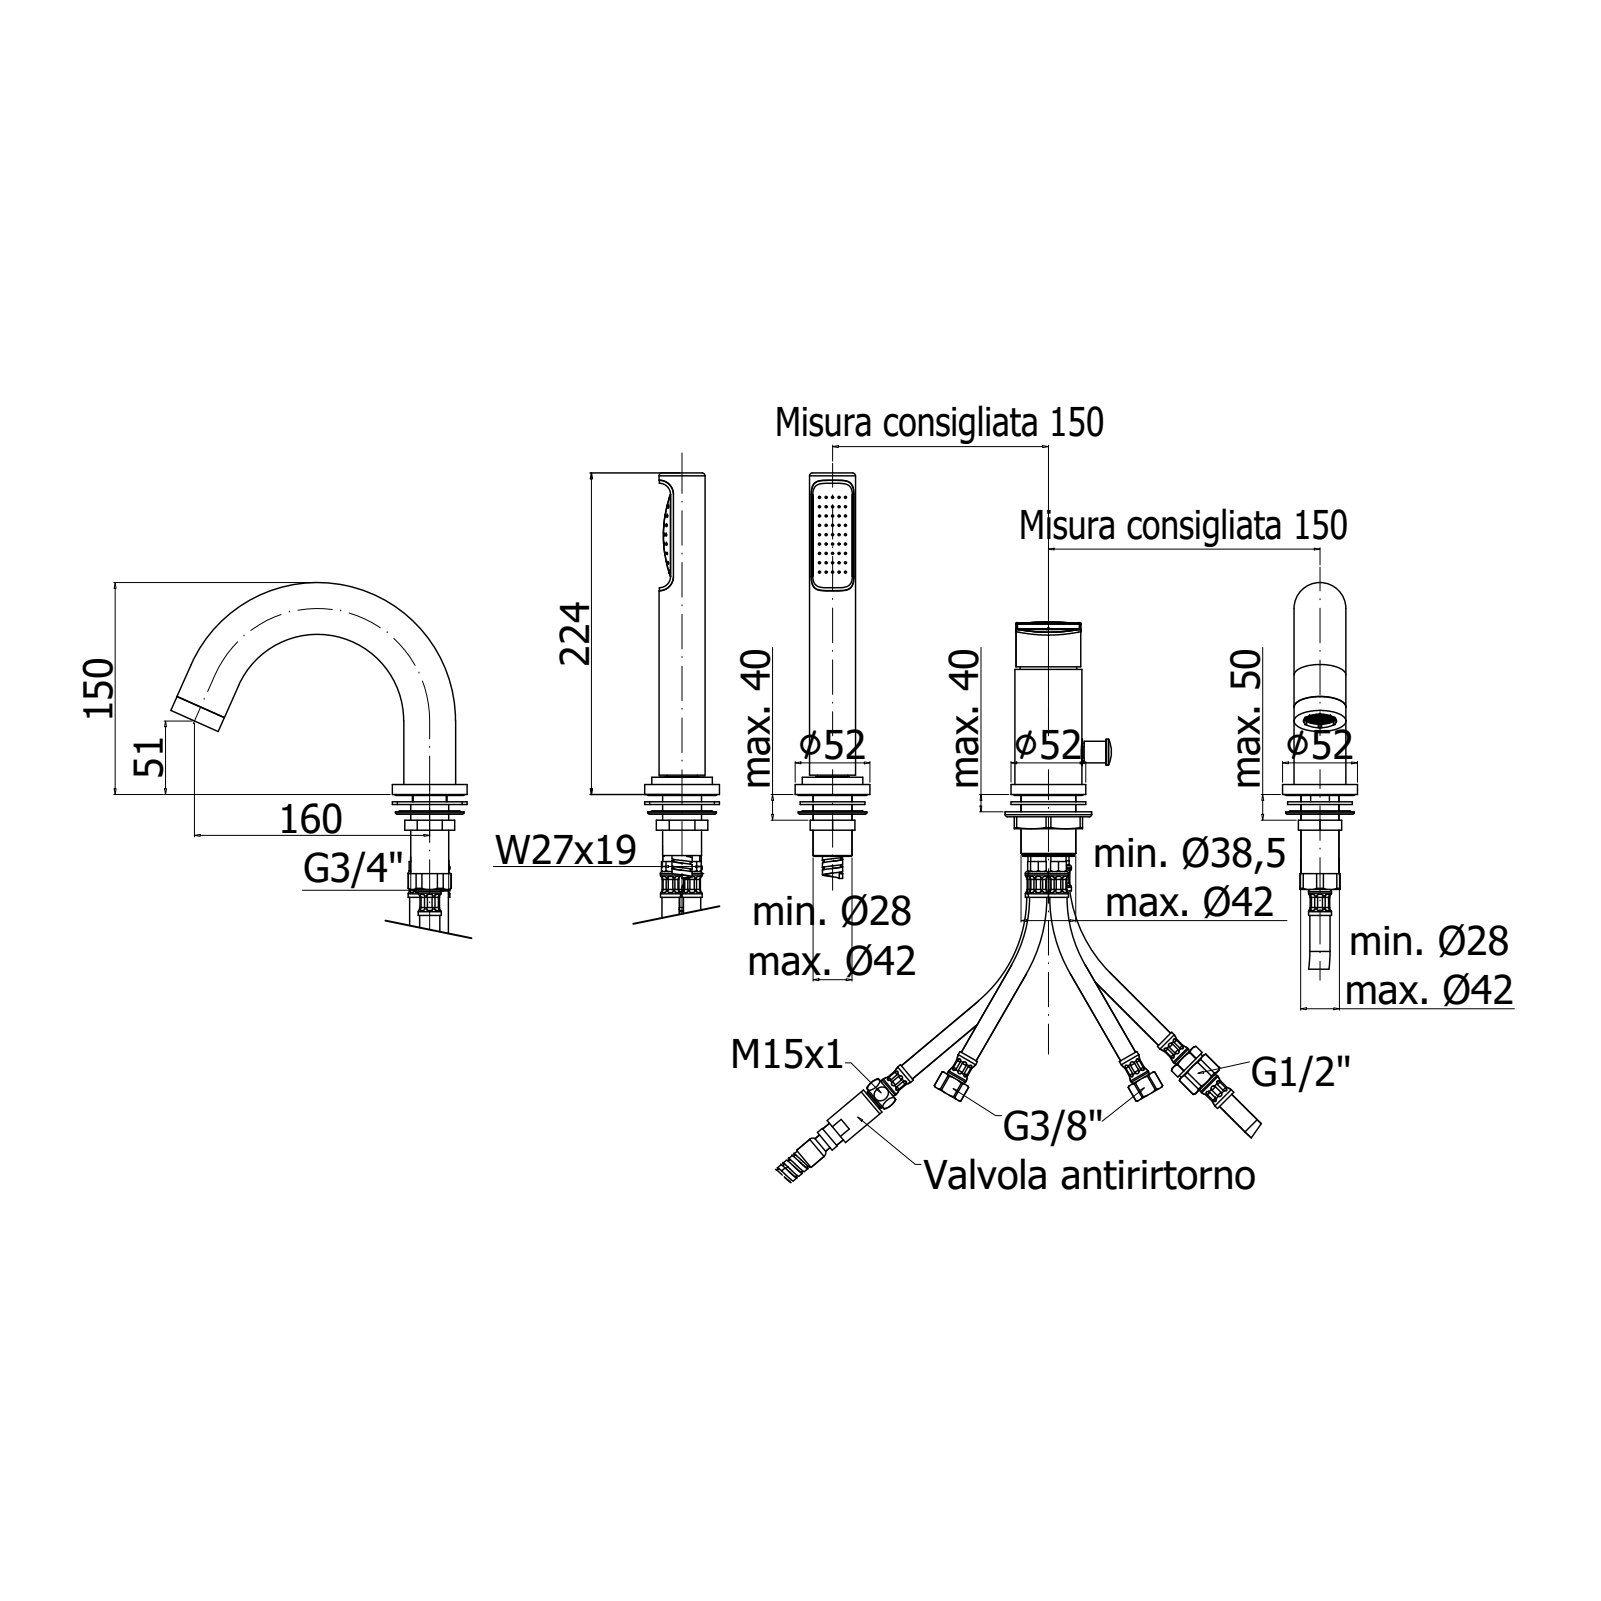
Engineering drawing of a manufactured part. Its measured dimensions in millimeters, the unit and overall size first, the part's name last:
Units: millimetres
Overall size (bounding box): 352 × 237.5 × 205.82
Round holes (diameter × count): ⌀7 ×6, ⌀5 ×2, ⌀3 ×1, ⌀3.5 ×1, ⌀4.5 ×1, ⌀6 ×1, ⌀7.2 ×1, ⌀9 ×1, ⌀9.5 ×1, ⌀13 ×1, ⌀13.5 ×1, ⌀15.2 ×1
Round bosses / shafts (diameter × count): ⌀52 ×3, ⌀36 ×2, ⌀46.5 ×1, ⌀45 ×1, ⌀42 ×1, ⌀32 ×1, ⌀21 ×1, ⌀18.5 ×1
Partial cylindrical surfaces — rounded edges, fillets, slot ends (radius × count): R3 ×4, R3.5 ×1, R8.5 ×1, R21.5 ×1
Main face-to-face distances: 7, 116.6, 109.6, 12, 5, 104.6, 44, 56, 49, 60.6
Hole centre spacings: 3, 8.6, 10.63, 13.45, 14, 14.32, 15.13, 18.11
Volume: 643 145 mm³ · Surface area: 116 141 mm²
Bodies: 5 solids, 291 faces (79 planar, 113 cylindrical, 99 other)
Part name (STEP PRODUCT): CA040CR
STEP written by: CREO PARAMETRIC BY PTC INC, 2020044 (CONFIG_CONTROL_DESIGN)
